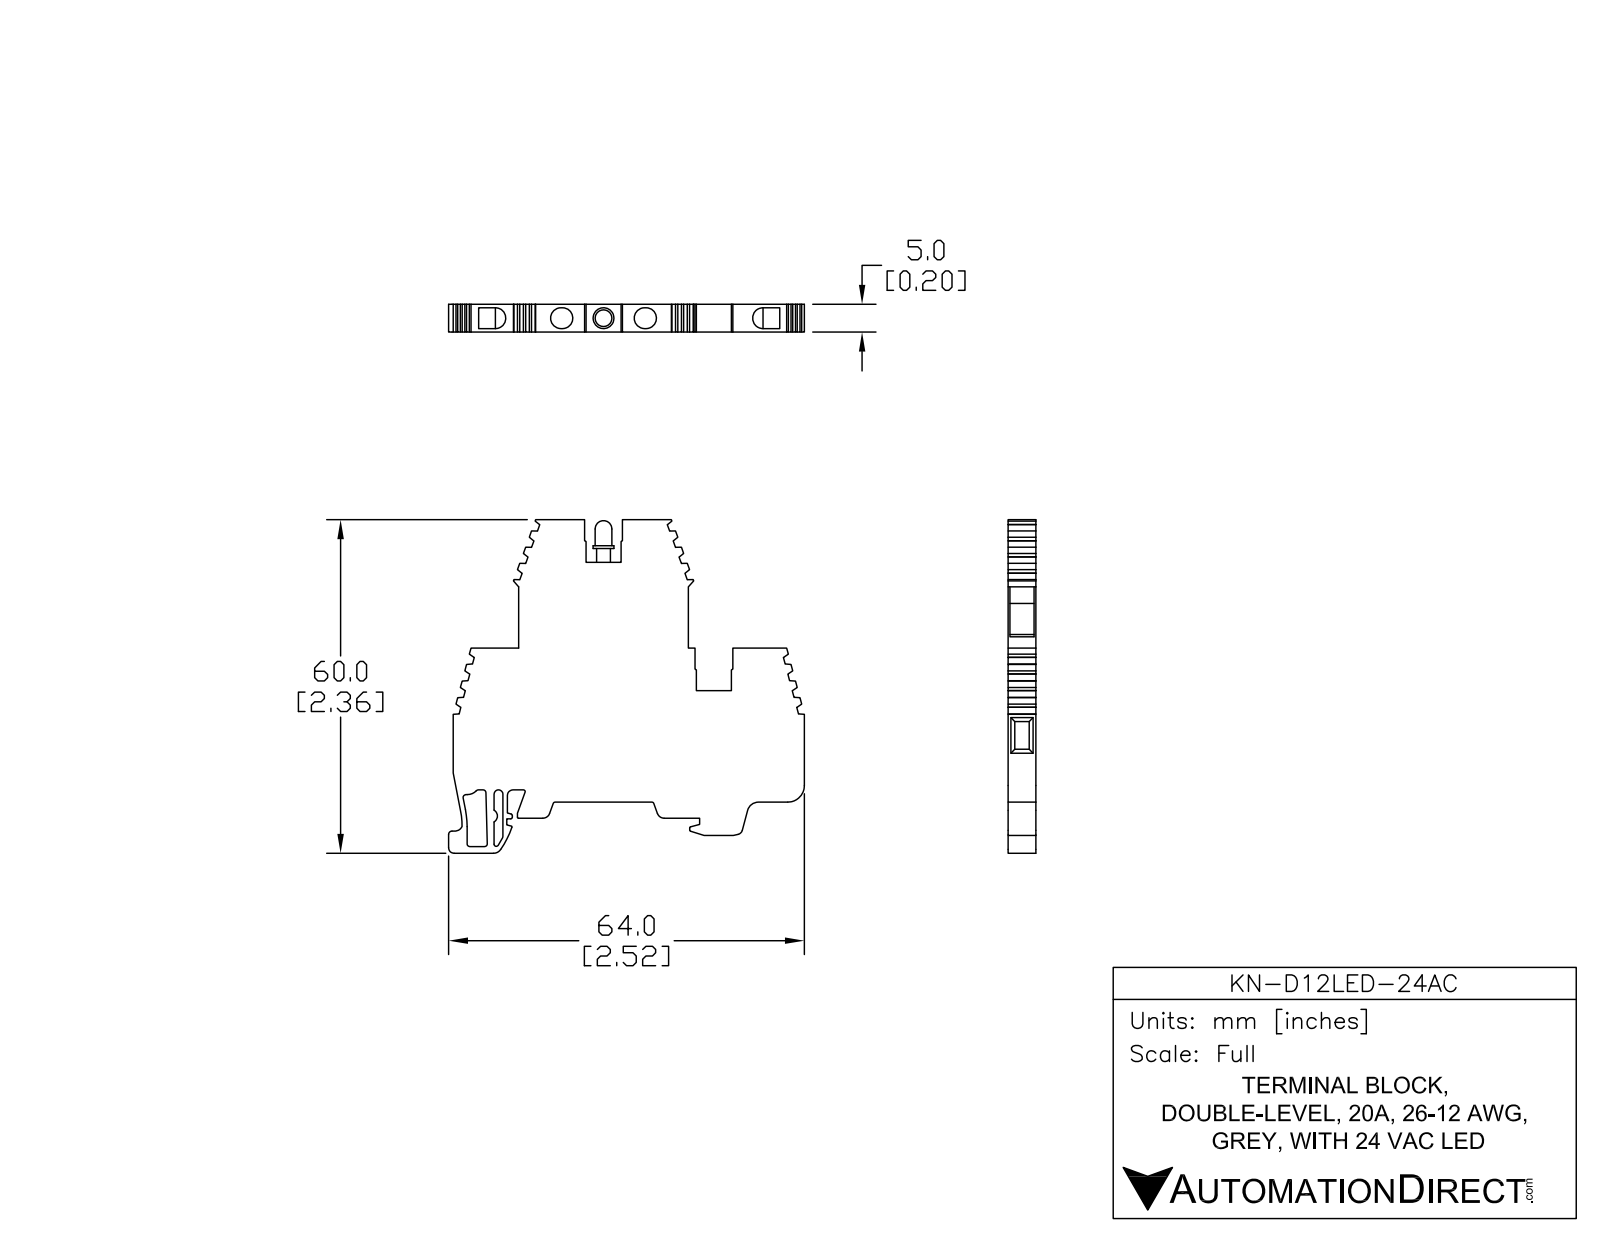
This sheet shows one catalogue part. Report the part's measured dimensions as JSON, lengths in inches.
{"part_name": "KN-D12LED-24AC", "step_written_by": "SolidWorks 2014 (AUTOMOTIVE_DESIGN)", "units": "inches", "bodies": {"solids": 3, "faces": 250, "planar": 200, "cylindrical": 49, "other": 1}, "overall_size": [2.521, 2.362, 0.197], "volume_in3": 0.696, "surface_area_in2": 11.04, "round_bosses_or_shafts": [[0.148, 1], [0.118, 1], [0.098, 1]], "partial_cylinders_radius": [[0.02, 7], [0.012, 6], [0.074, 6], [0.008, 3], [0.039, 3], [0.024, 2], [0.016, 1], [0.031, 1]], "face_to_face_distances": [0.197, 0.184, 0.013, 0.115, 0.909, 0.157, 0.258, 0.782, 0.248, 0.302]}
